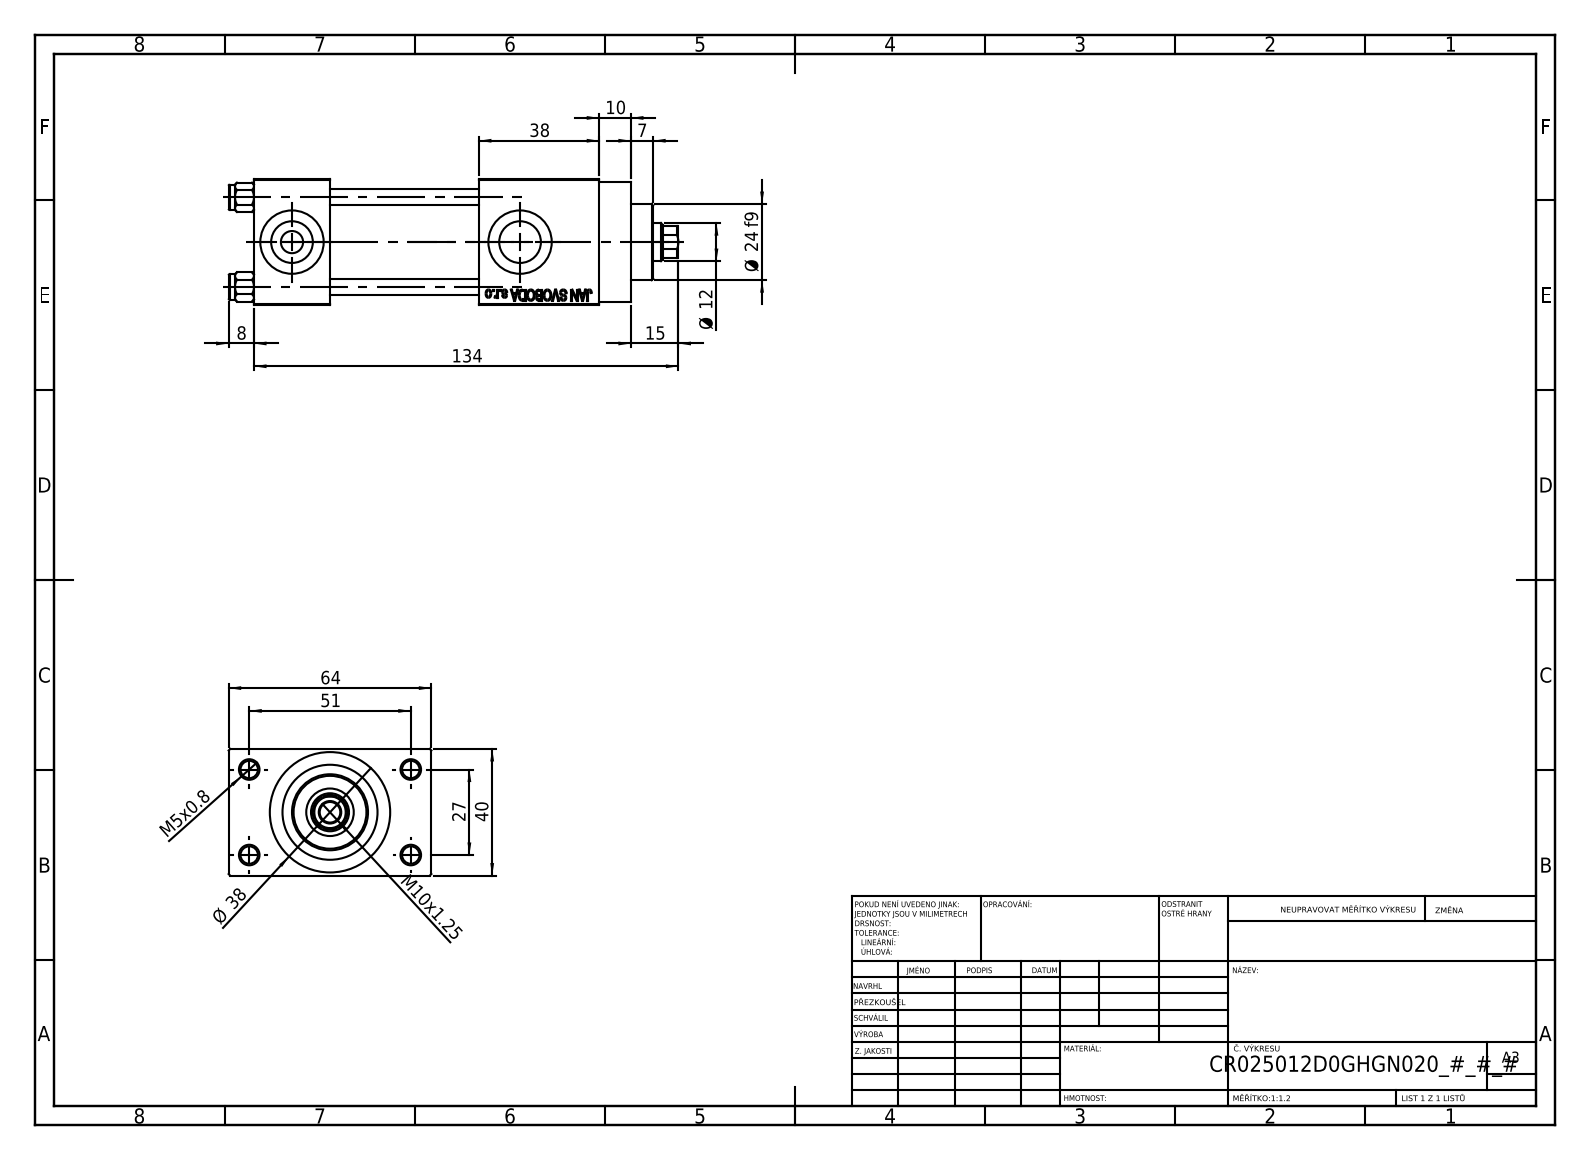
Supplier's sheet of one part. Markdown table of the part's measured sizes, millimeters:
| quantity | value |
| --- | --- |
| part name | V215_VC_A; V215CR_VCP_D; V215CR_D_Body; NUT_M5_D (+1 more) |
| STEP written by | SolidWorks 2019 (CONFIG_CONTROL_DESIGN) |
| units | millimeters |
| bodies | 11 solids, 1102 faces (496 planar, 88 cylindrical, 518 other) |
| overall size | 142 × 64 × 40 |
| volume | 173 683 mm³ |
| surface area | 62 160 mm² |
| round holes (diameter × count) | 5 × 4, 5.5 × 4, 20 × 3, 7 × 2, 13.16 × 2, 6.5 × 1, 12 × 1, 15 × 1, 25 × 1, 30 × 1 |
| round bosses / shafts (diameter × count) | 8 × 4, 38 × 1, 31 × 1, 24 × 1 |
| partial cylindrical surfaces (radius × count) | 5.5 × 1 |
| main face-to-face distances | 40, 12, 47, 24, 71, 52, 38, 109, 85, 64 |
| hole center spacings | 11.37, 20.01, 28.3, 28.85, 29.89, 39.66, 48.34, 27 |
